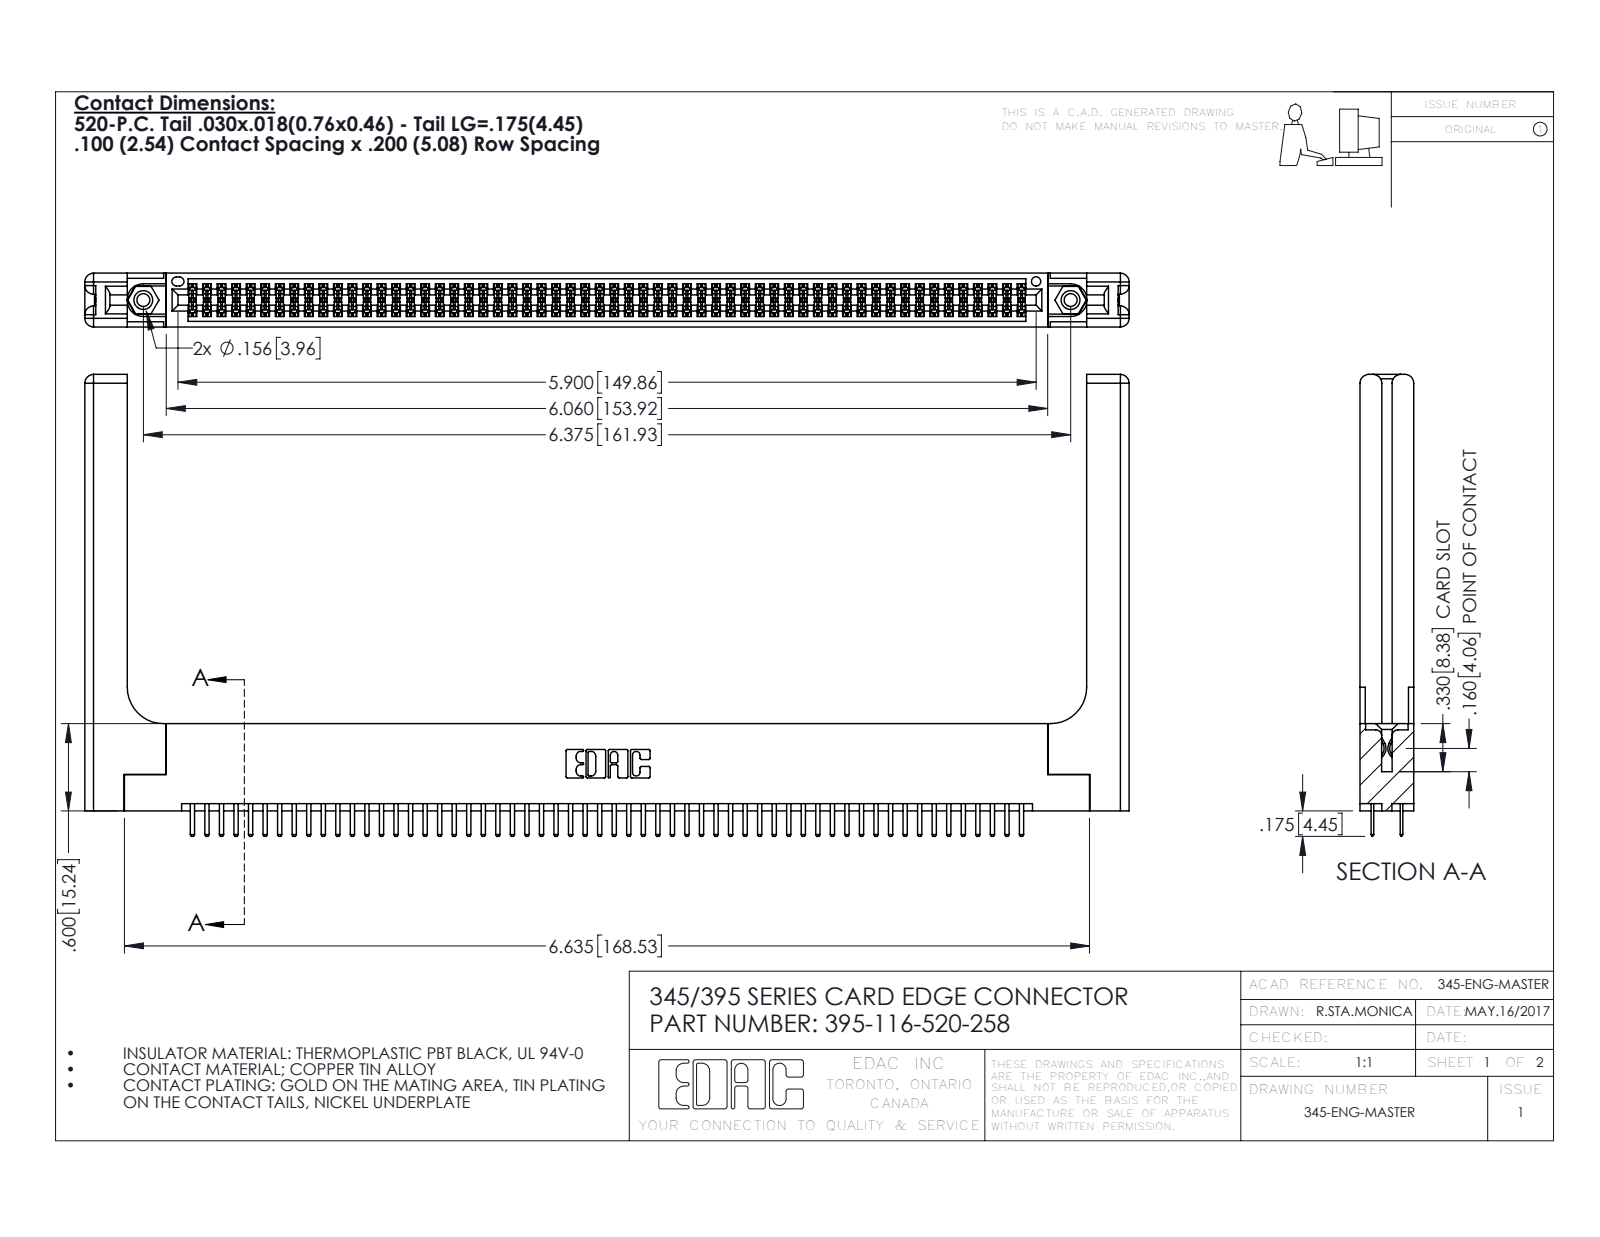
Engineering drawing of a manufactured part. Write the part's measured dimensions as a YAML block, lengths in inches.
part_name: "345 Part_Flush Mounting Lugs - 0.156 Dia-TH; 345-250-001_345-250-001-102; 395-116-520-258; 345-220-058_345-220-058 (+1 more)"
step_written_by: "SolidWorks 2016 (CONFIG_CONTROL_DESIGN)"
units: inches
bodies: {solids: 121, faces: 6646, planar: 4288, cylindrical: 2298, other: 60}
overall_size: [7.179, 3.175, 0.37]
volume: 1.604
surface_area: 48.96
round_holes:
  - {diameter: 0.089, count: 2}
  - {diameter: 0.125, count: 2}
  - {diameter: 0.156, count: 2}
  - {diameter: 0.064, count: 1}
round_bosses_or_shafts:
  - {diameter: 0.155, count: 2}
partial_cylinders:
  - {radius: 0.006, count: 174}
  - {radius: 0.01, count: 120}
  - {radius: 0.01, count: 22}
  - {radius: 0.06, count: 16}
  - {radius: 0.007, count: 6}
  - {radius: 0.031, count: 6}
  - {radius: 0.026, count: 3}
  - {radius: 0.014, count: 2}
face_to_face_distances: [0.072, 0.298, 0.37, 0.2, 0.098, 0.272, 0.025, 0.225, 0.022, 0.072]
hole_center_spacings: [0.27, 6.139, 6.375]
